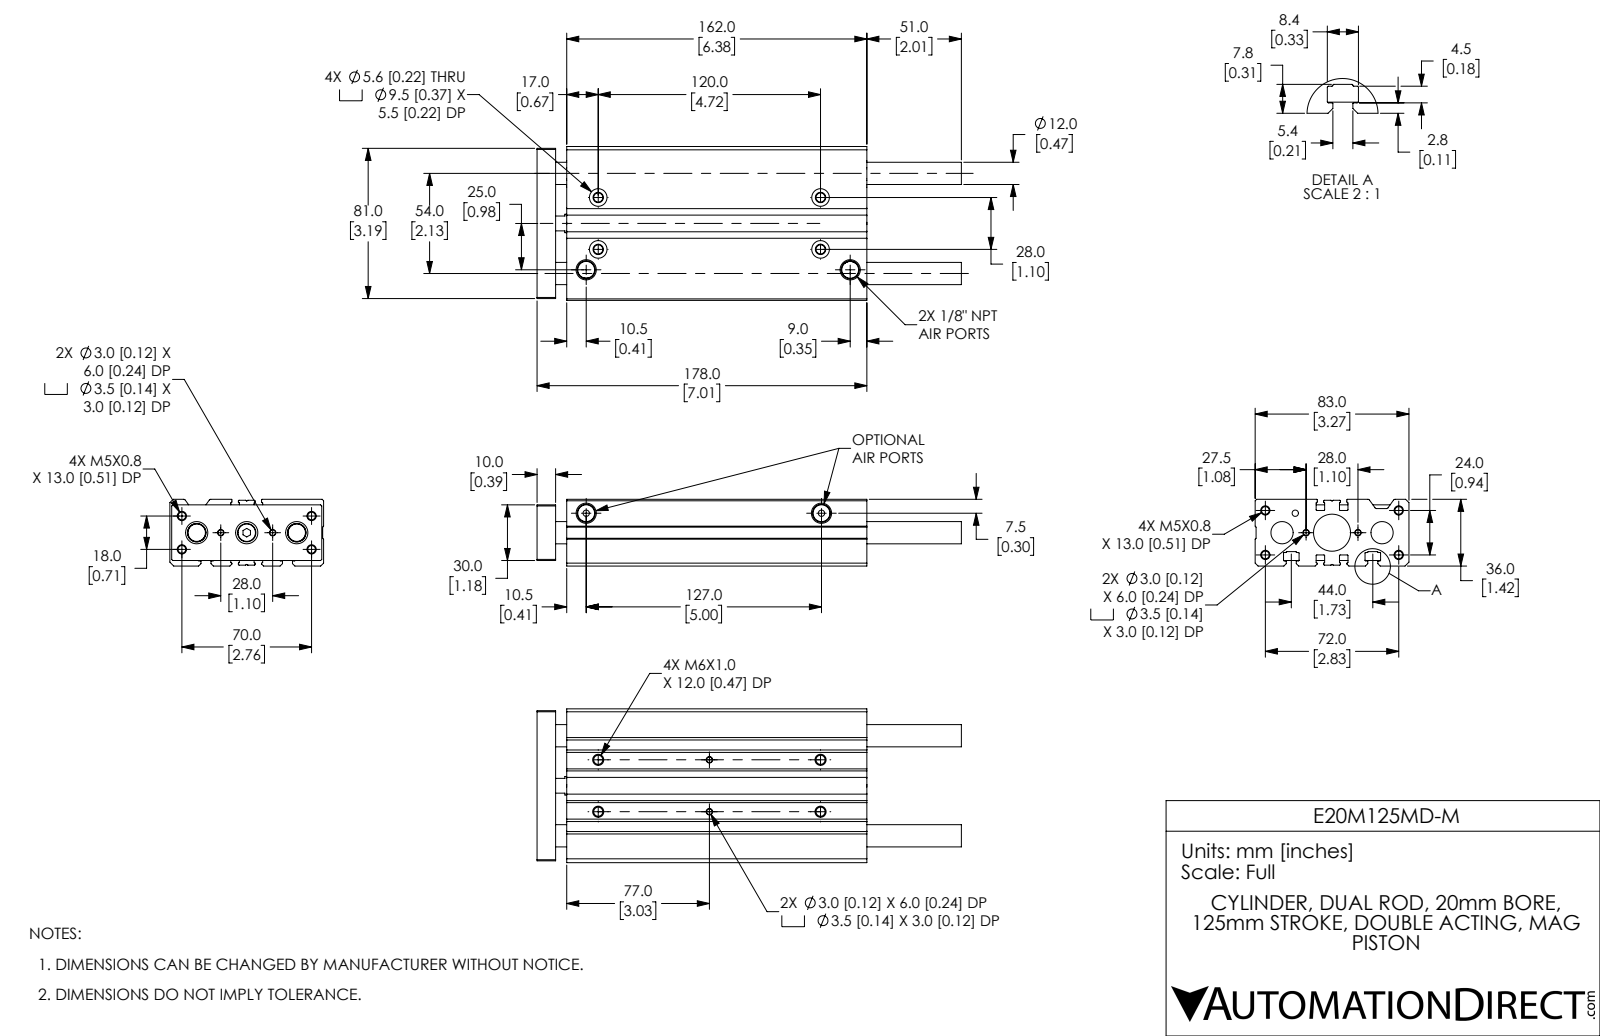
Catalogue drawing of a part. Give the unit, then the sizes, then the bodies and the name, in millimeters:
Units: millimetres
Overall size (bounding box): 229 × 83 × 36
Round holes (diameter × count): ⌀4.13 ×8, ⌀3 ×4, ⌀3.5 ×4, ⌀4.92 ×4, ⌀5.6 ×4, ⌀9.5 ×4, ⌀6 ×3, ⌀12 ×3, ⌀3.43 ×2, ⌀9.91 ×2, ⌀3.43 ×1, ⌀12 ×1
Round bosses / shafts (diameter × count): ⌀10 ×1, ⌀9.91 ×1
Partial cylindrical surfaces — rounded edges, fillets, slot ends (radius × count): R0.4 ×20, R0.2 ×18, R0.3 ×10, R0.25 ×8, R1 ×4
Main face-to-face distances: 36, 0.5, 6, 83, 3, 30, 22.2, 45.5, 28.2, 37.5
Hole centre spacings: 3.16, 12.04, 15, 21.02, 22.85, 25.06, 28, 36.14
Volume: 435 811 mm³ · Surface area: 118 374 mm²
Bodies: 5 solids, 405 faces (128 planar, 182 cylindrical, 95 other)
Part name (STEP PRODUCT): E20M125MD-M_ENDPLATE; E20M125MD-M; E20M125MD-M_BODY
STEP written by: SolidWorks 2019 (CONFIG_CONTROL_DESIGN)
